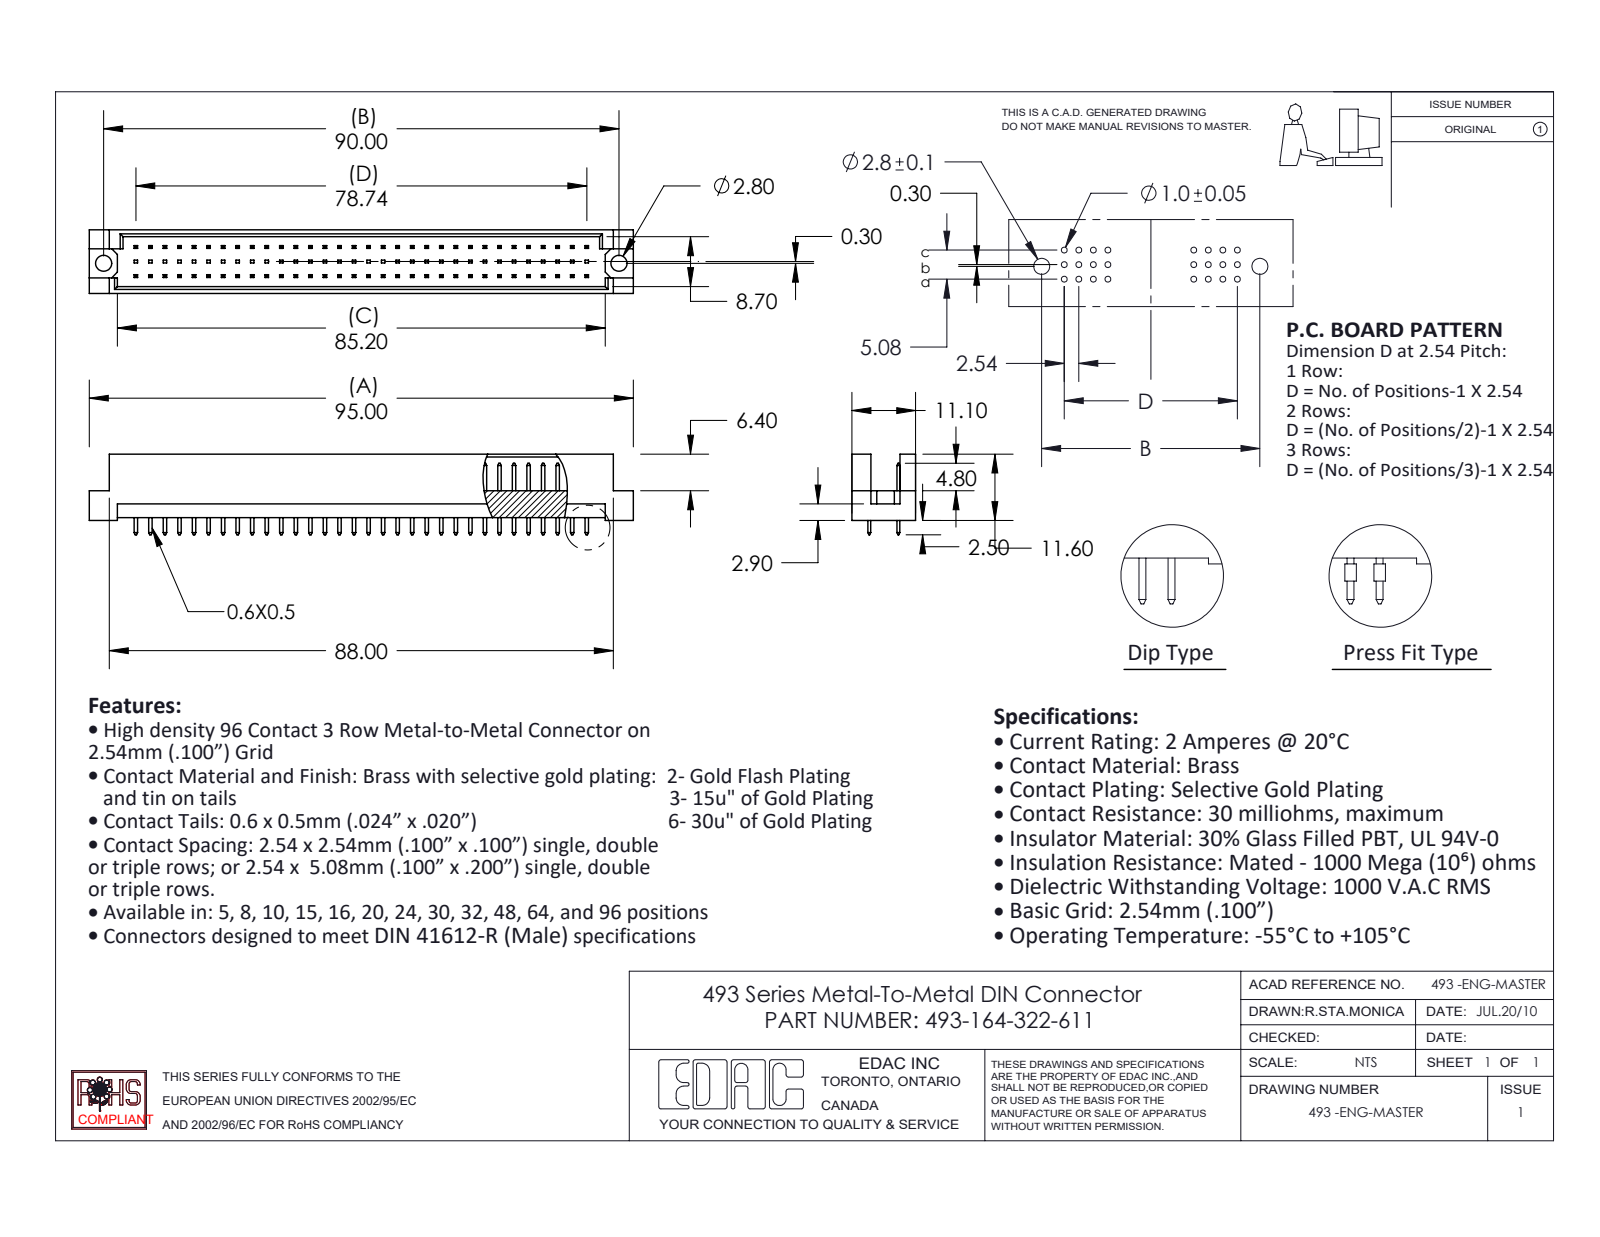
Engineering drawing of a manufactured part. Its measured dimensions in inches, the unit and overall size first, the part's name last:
Units: inches
Overall size (bounding box): 3.74 × 0.555 × 0.437
Round holes (diameter × count): ⌀0.11 ×2
Main face-to-face distances: 0.047, 0.39, 0.437, 0.2, 0.343, 0.02, 0.185, 0.109, 0.128, 0.309
Hole centre spacings: 3.543
Volume: 0.36 in³ · Surface area: 12.73 in²
Bodies: 65 solids, 1332 faces (1328 planar, 4 cylindrical, 0 other)
Part name (STEP PRODUCT): 493-290_22; 493 Part_96; 493-164-322-611
STEP written by: SolidWorks 2020 (CONFIG_CONTROL_DESIGN)
